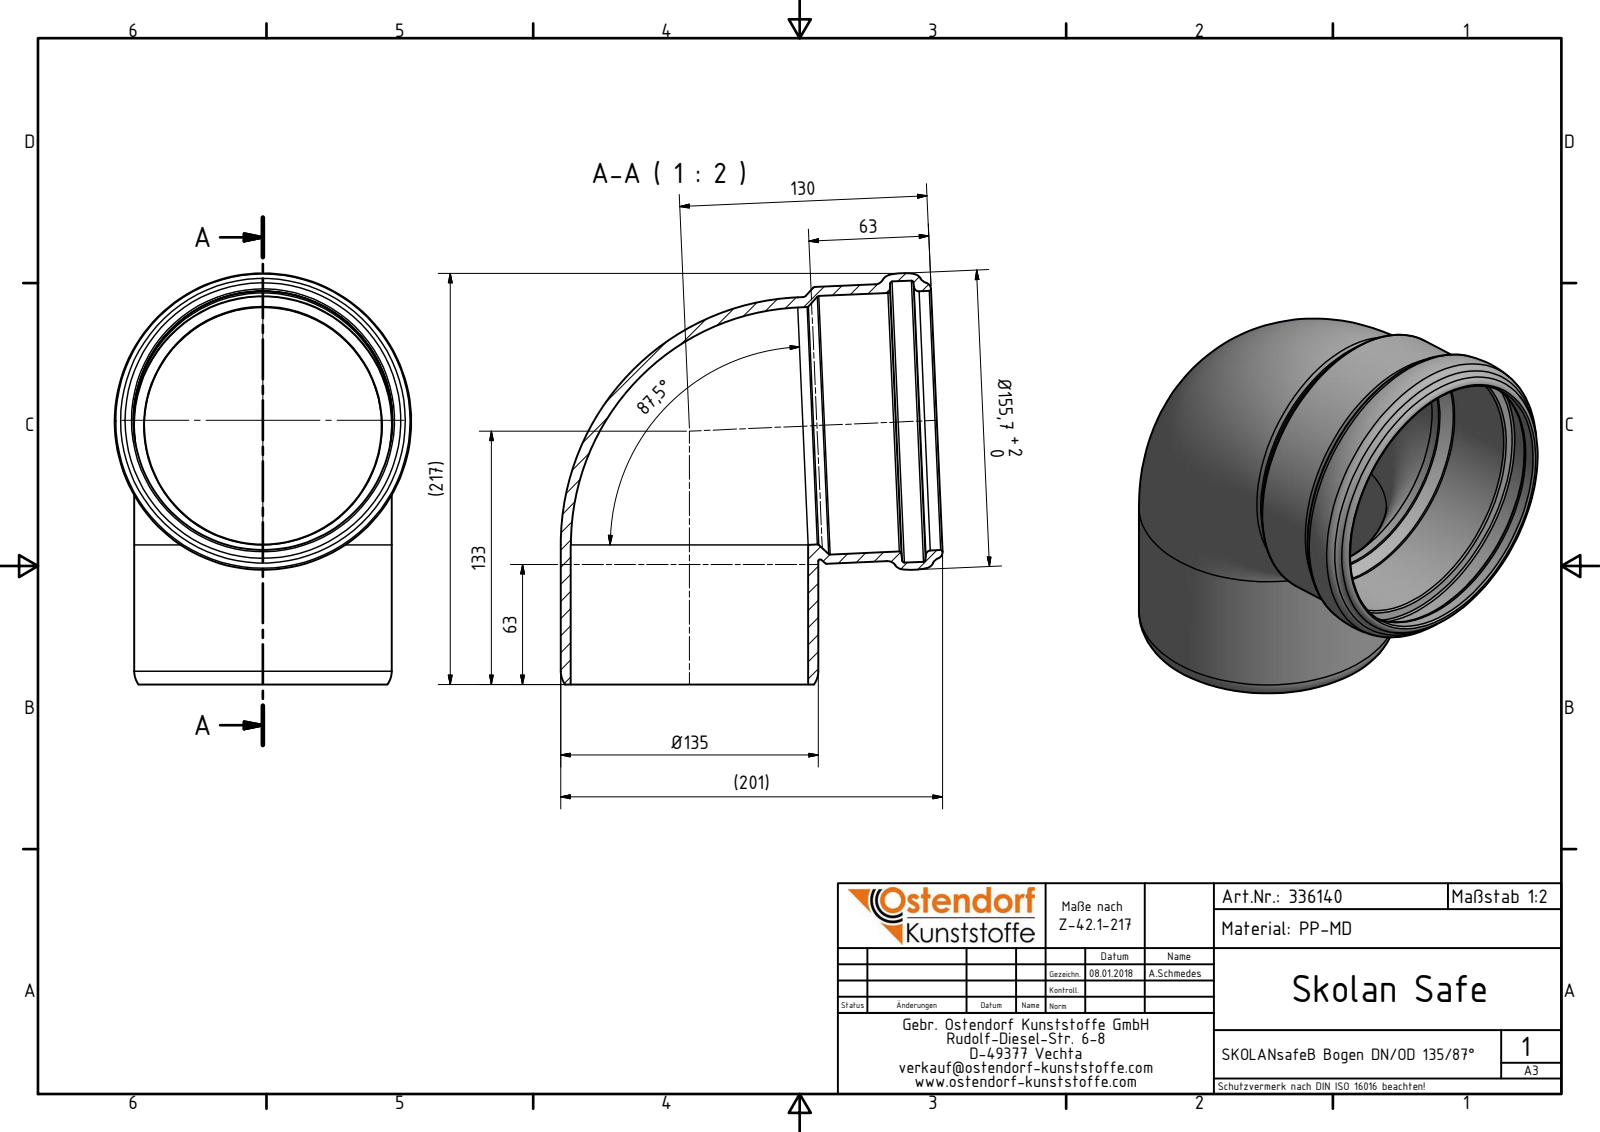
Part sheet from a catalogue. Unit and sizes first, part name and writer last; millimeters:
Units: millimetres
Overall size (bounding box): 215.82 × 200.54 × 155.7
Round holes (diameter × count): ⌀124.7 ×2, ⌀135.8 ×1, ⌀136.1 ×1, ⌀147.7 ×1
Round bosses / shafts (diameter × count): ⌀135.3 ×2, ⌀145.4 ×1
Volume: 502 309 mm³ · Surface area: 210 243 mm²
Bodies: 1 solid, 44 faces (1 planar, 8 cylindrical, 35 other)
Part name (STEP PRODUCT): 336140 SKOLANsafeB Bogen DN_OD 135_87°
STEP written by: Autodesk Inventor 2016 (AUTOMOTIVE_DESIGN)
